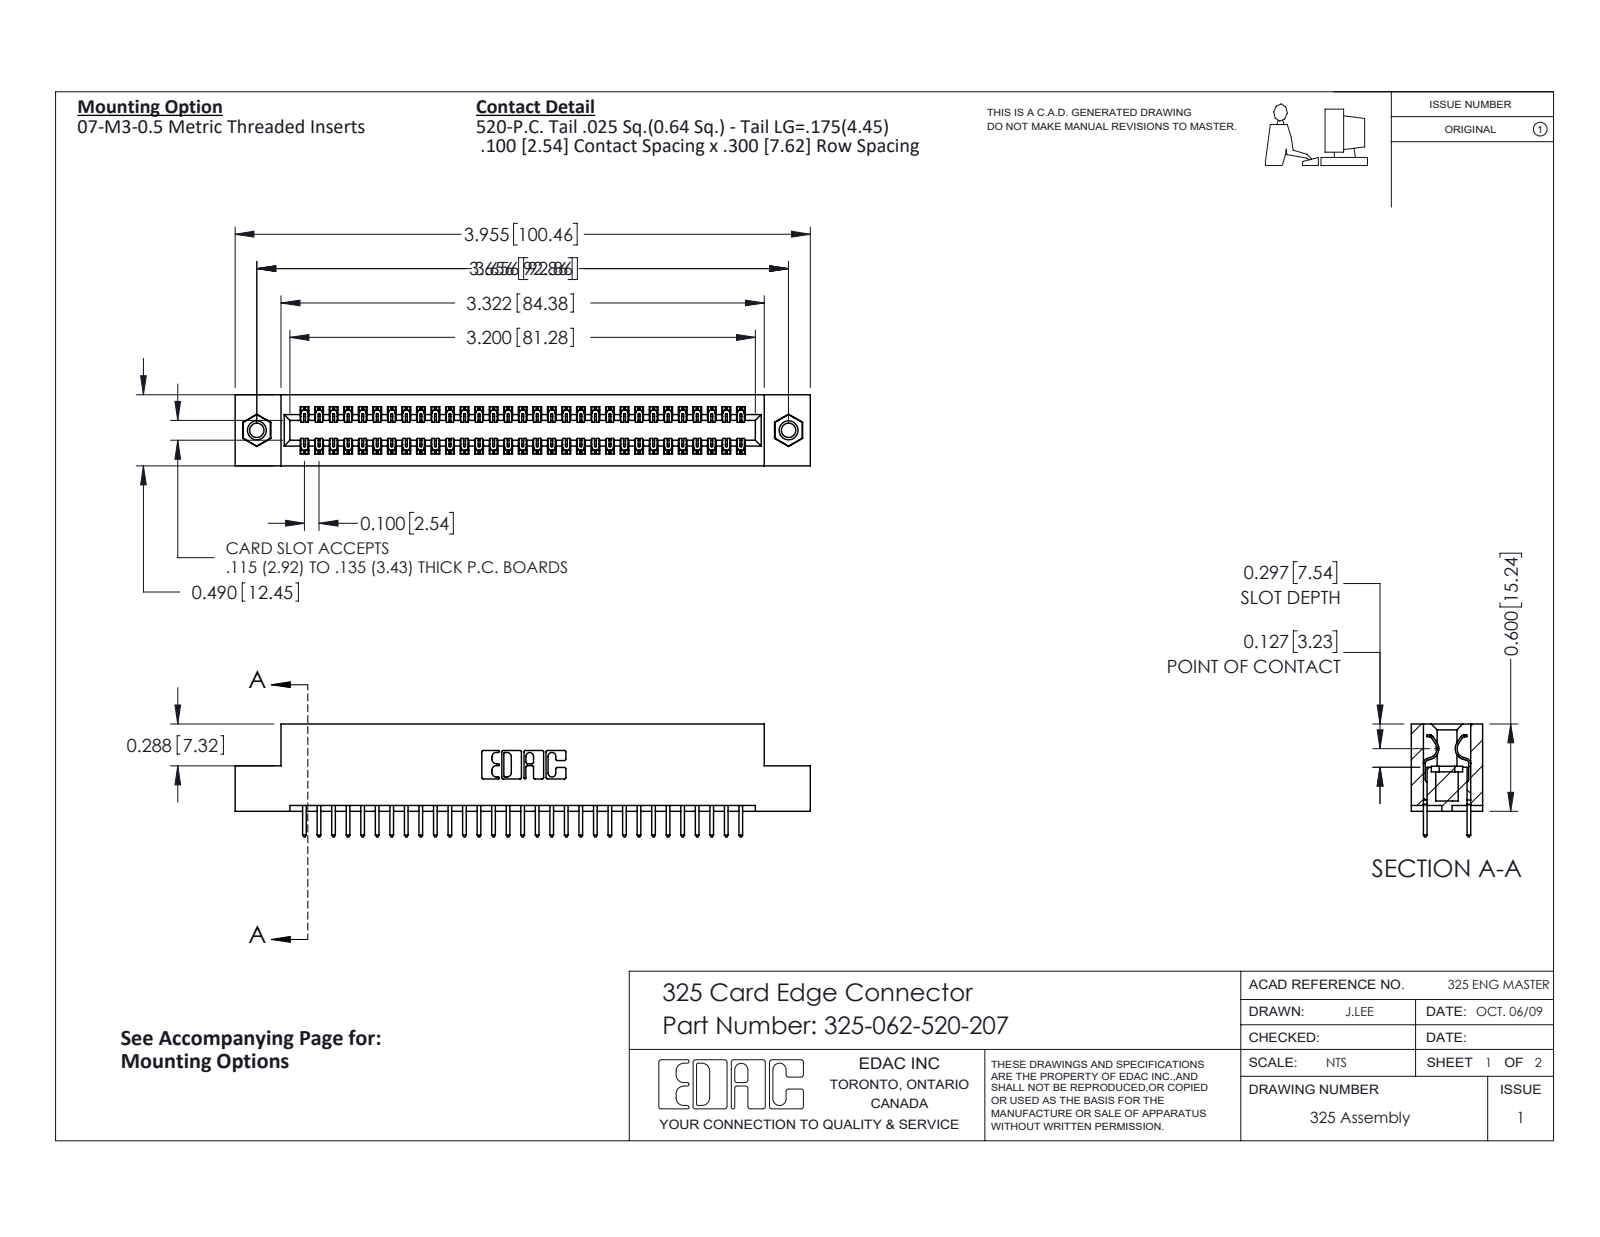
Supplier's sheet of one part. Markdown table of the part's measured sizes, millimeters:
| quantity | value |
| --- | --- |
| part name | 325 Part_TI; 345-250-001_345-250-005-103; 325-292-001_325-293-120; 325-062-520-207 |
| STEP written by | SolidWorks 2016 (CONFIG_CONTROL_DESIGN) |
| units | millimeters |
| bodies | 65 solids, 3398 faces (2334 planar, 1048 cylindrical, 16 other) |
| overall size | 100.5 × 19.7 × 12.4 |
| volume | 12 800 mm³ |
| surface area | 15 190 mm² |
| round holes (diameter × count) | 2.5 × 2, 3.2 × 2, 4.1 × 2 |
| round bosses / shafts (diameter × count) | 3.9 × 2 |
| partial cylindrical surfaces (radius × count) | 0.2 × 93, 0.3 × 62, 0.3 × 22, 0.2 × 6, 0.8 × 6, 0.7 × 3, 0.4 × 2, 0.6 × 2 |
| main face-to-face distances | 2.1, 10.3, 7.6, 12.4, 2.7, 9.7, 0.6, 8.3, 1, 7 |
| hole center spacings | 92.9 |
